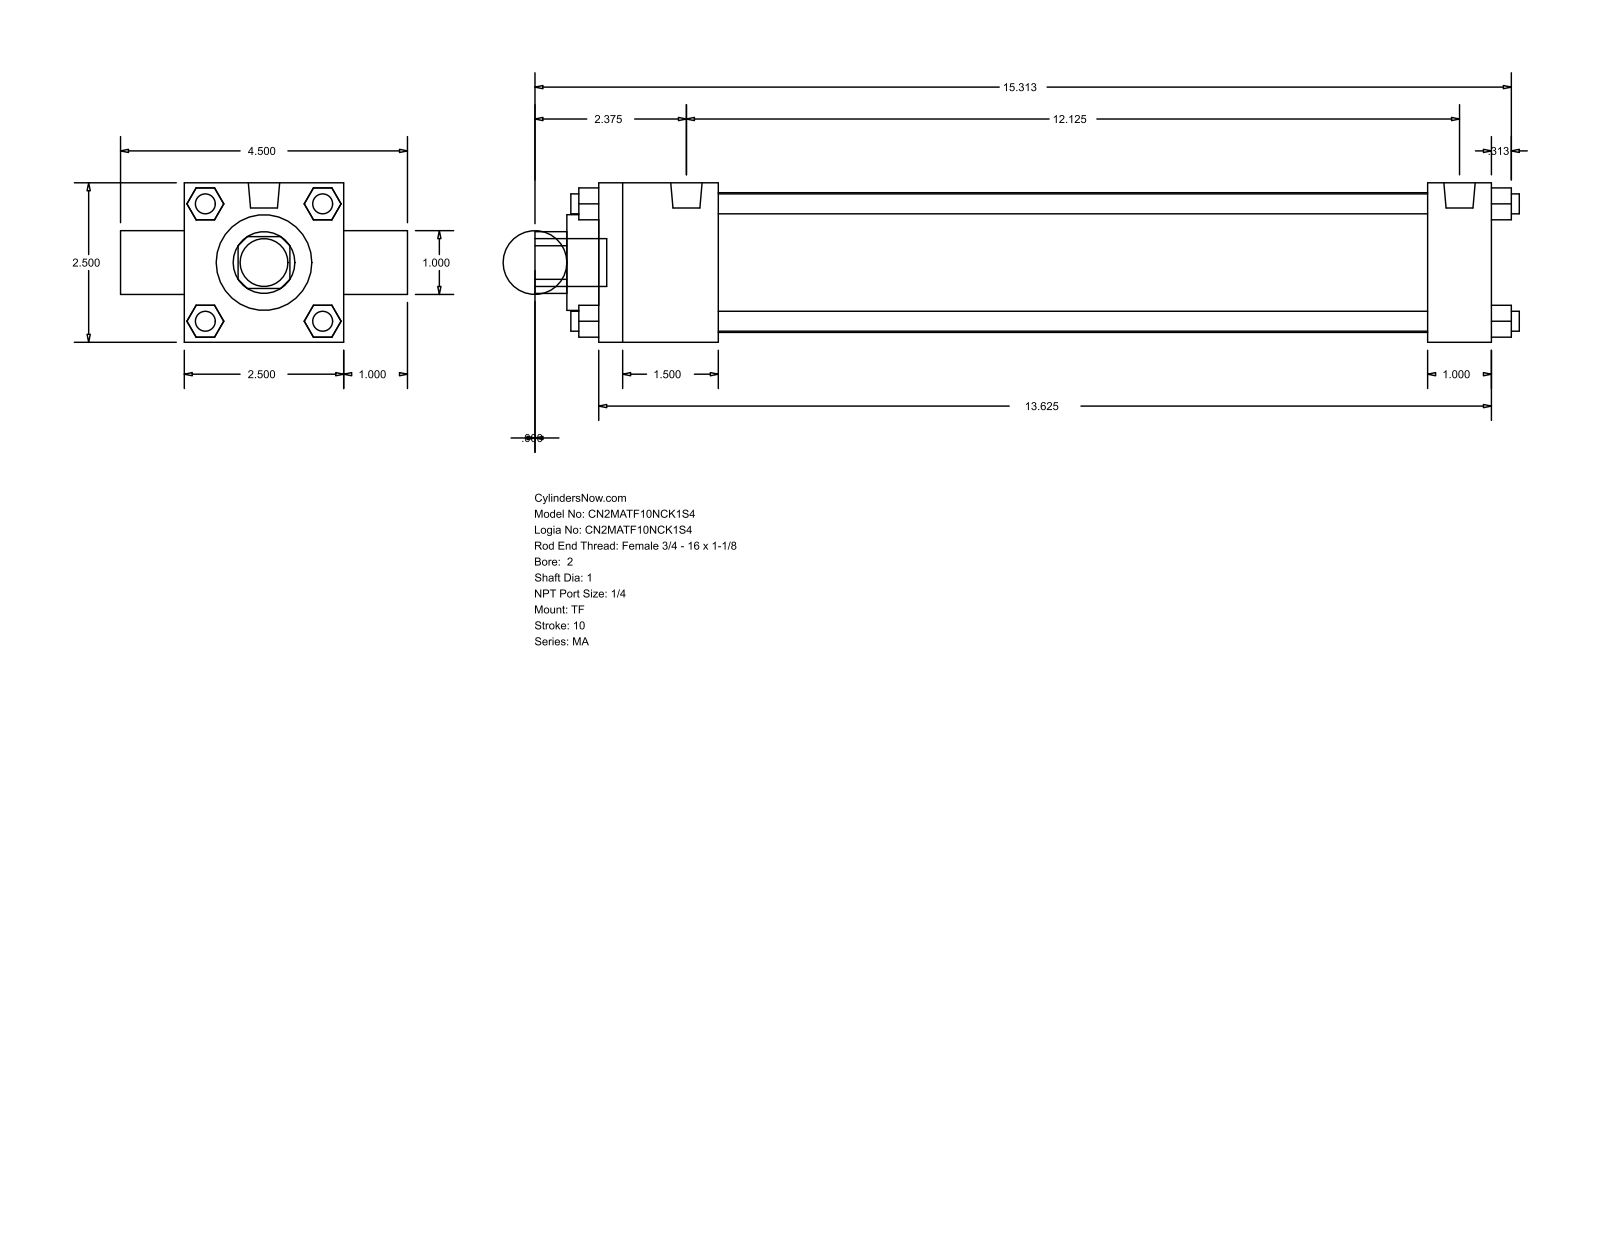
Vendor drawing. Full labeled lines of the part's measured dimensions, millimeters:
Part name (STEP PRODUCT): MA_TF__0200_1
STEP written by: GSSL Pune (CONFIG_CONTROL_DESIGN)
Units: millimetres
Bodies: 0 solids, 120 faces (92 planar, 28 cylindrical, 0 other)
Overall size (bounding box): 392.11 × 114.3 × 63.5
Round holes (diameter × count): ⌀25.4 ×2, ⌀38.1 ×1, ⌀55.63 ×1
Round bosses / shafts (diameter × count): ⌀7.94 ×7, ⌀12.49 ×2, ⌀19.05 ×1
Partial cylindrical surfaces — rounded edges, fillets, slot ends (radius × count): R12.29 ×1
Main face-to-face distances: 63.5, 25.4, 355.6, 12.7, 47.63, 330.2, 282.57, 307.97, 88.9, 23.37
